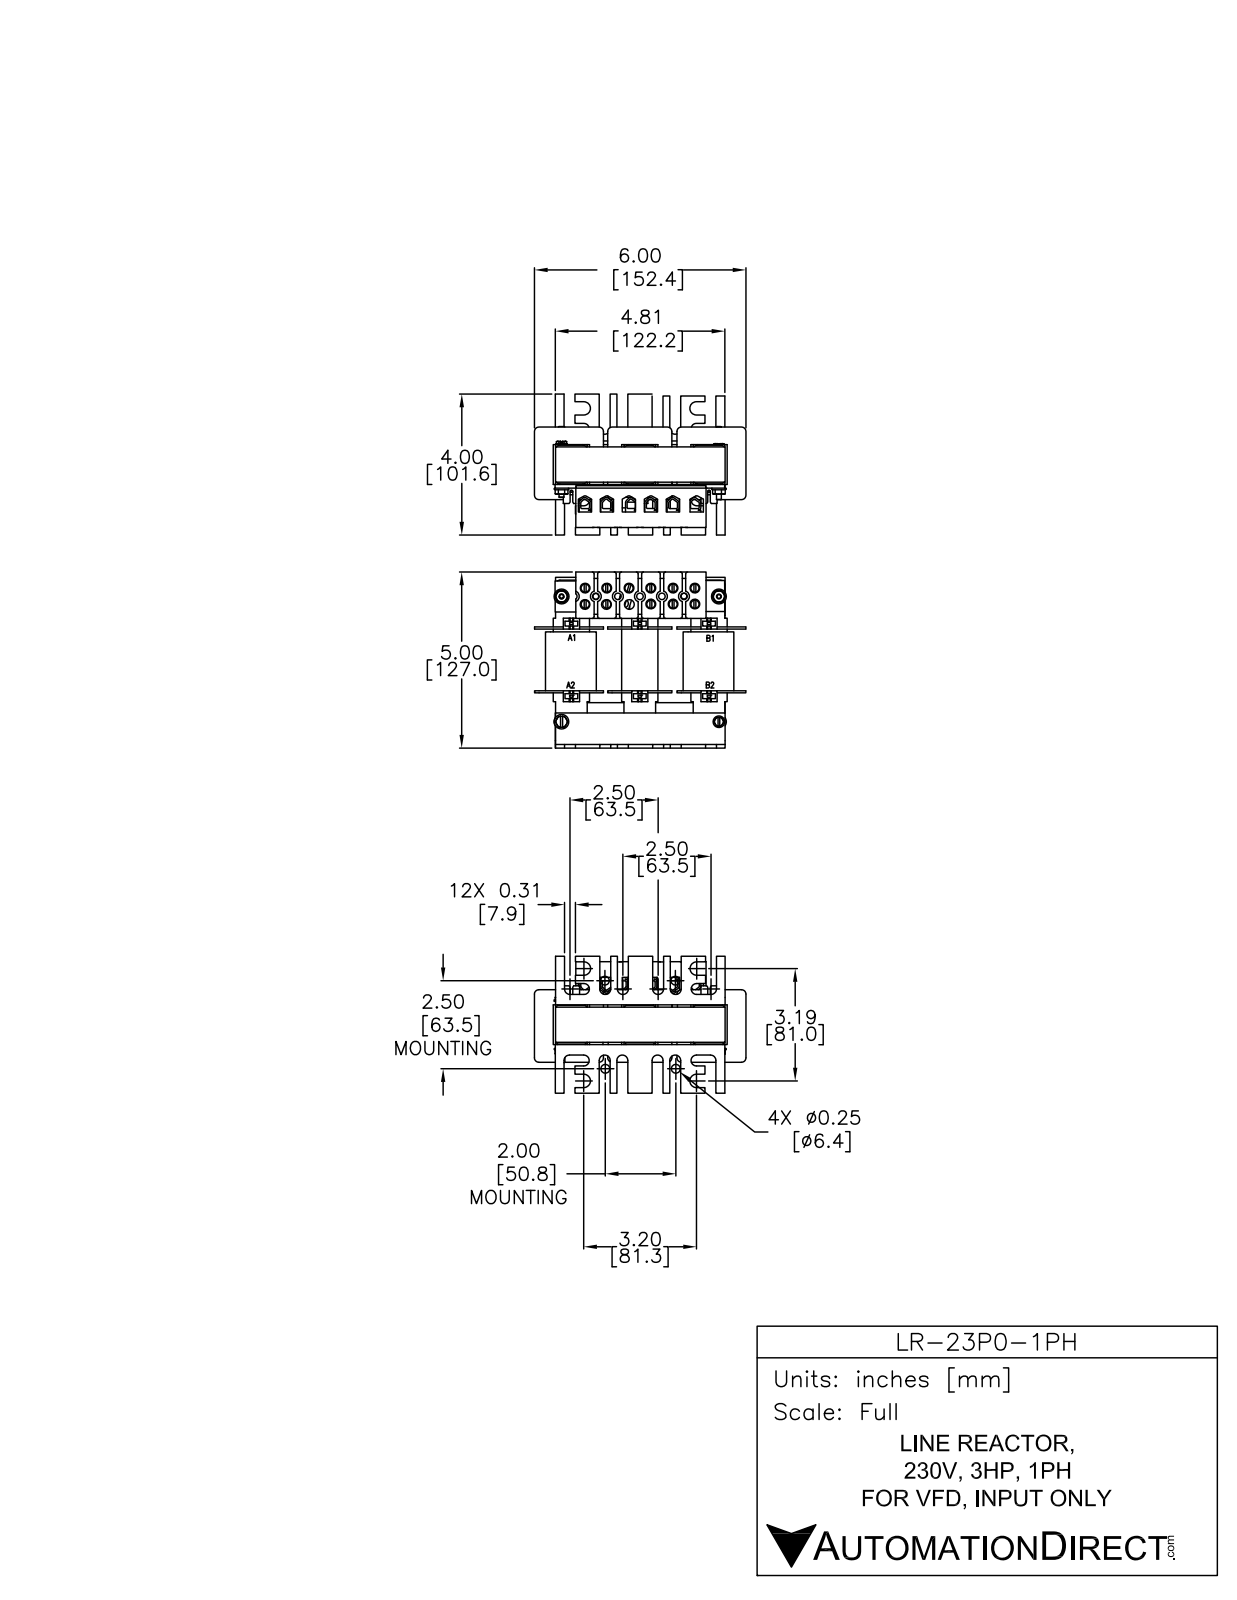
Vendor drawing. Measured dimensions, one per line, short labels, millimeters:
name: LR-23P0-1PH
written by: SolidWorks 2011 (AUTOMOTIVE_DESIGN)
unit: mm
bodies: 43 solids, 1048 faces (794 planar, 222 cylindrical, 32 other)
size: 144.75 × 131.2 × 98.38
volume: 540 879 mm³; area: 167 068 mm²
holes: 12× ⌀7, 5× ⌀7.75
bosses: 12× ⌀7, 4× ⌀10.25, 4× ⌀8, 2× ⌀7.75, 2× ⌀7.5, 2× ⌀3.4, 2× ⌀3.25
rounds: 16× R3.94, 12× R1.82, 12× R2.68, 12× R2.71, 12× R5, 12× R6, 4× R4.83, 3× R0.86
face distances: 2.5, 27.26, 1.5, 31.25, 5.62, 34.88, 28.76, 34.38, 7.12, 32.88
hole spacings: 16, 32, 21.26, 34.93, 48, 14, 50, 10.34
